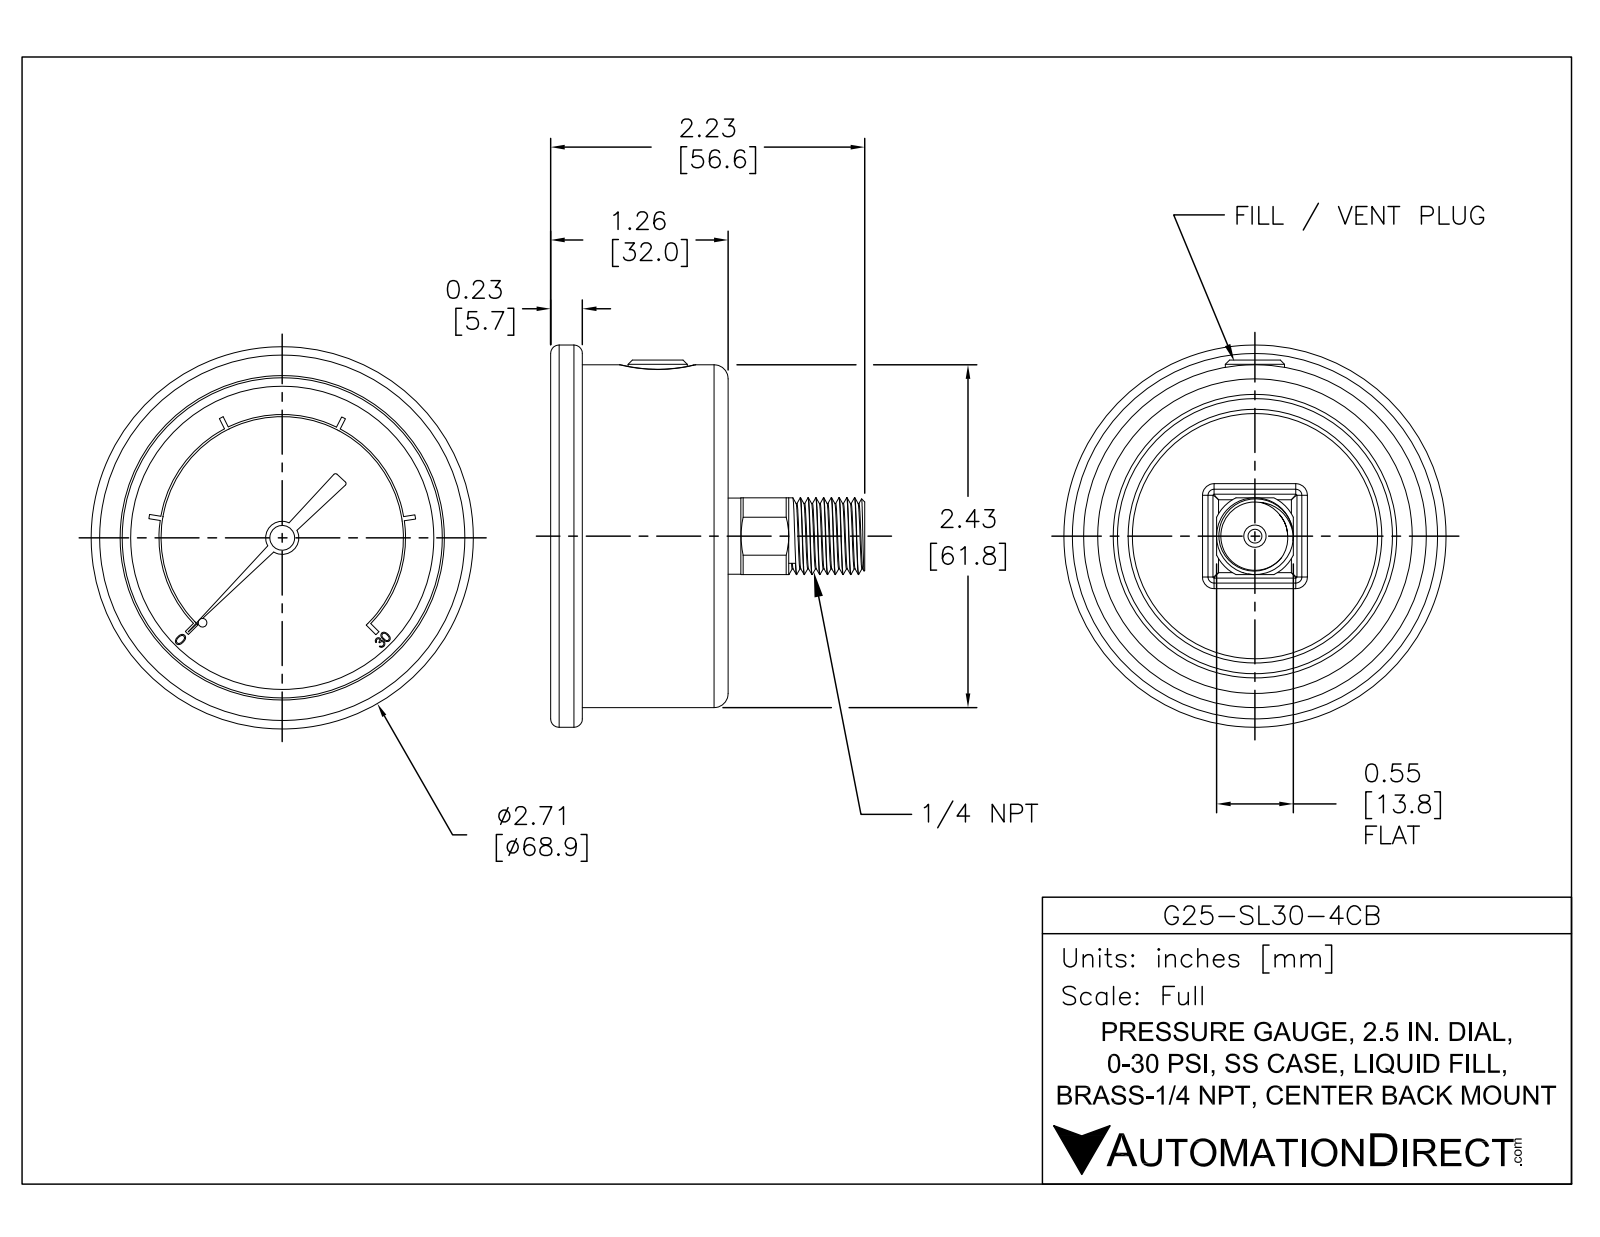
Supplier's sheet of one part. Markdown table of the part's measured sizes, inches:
| quantity | value |
| --- | --- |
| part name | G25-SL30-4CB |
| STEP written by | SolidWorks 2021 (AUTOMOTIVE_DESIGN) |
| units | inches |
| bodies | 1 solid, 348 faces (203 planar, 83 cylindrical, 62 other) |
| overall size | 2.713 × 2.713 × 2.23 |
| volume | 5.168 in³ |
| surface area | 24.82 in² |
| round holes (diameter × count) | 0.071 × 1, 0.098 × 1, 2.272 × 1 |
| round bosses / shafts (diameter × count) | 2.713 × 1, 2.433 × 1, 0.545 × 1, 0.54 × 1, 0.42 × 1, 0.235 × 1, 0.176 × 1, 0.14 × 1 |
| partial cylindrical surfaces (radius × count) | 0.06 × 8, 0.015 × 2, 0.304 × 1, 0.86 × 1, 0.875 × 1 |
| main face-to-face distances | 0.95, 1.2, 0.25, 0.06, 1.01, 1.26, 1.035, 0.975, 0.025, 0.225 |
